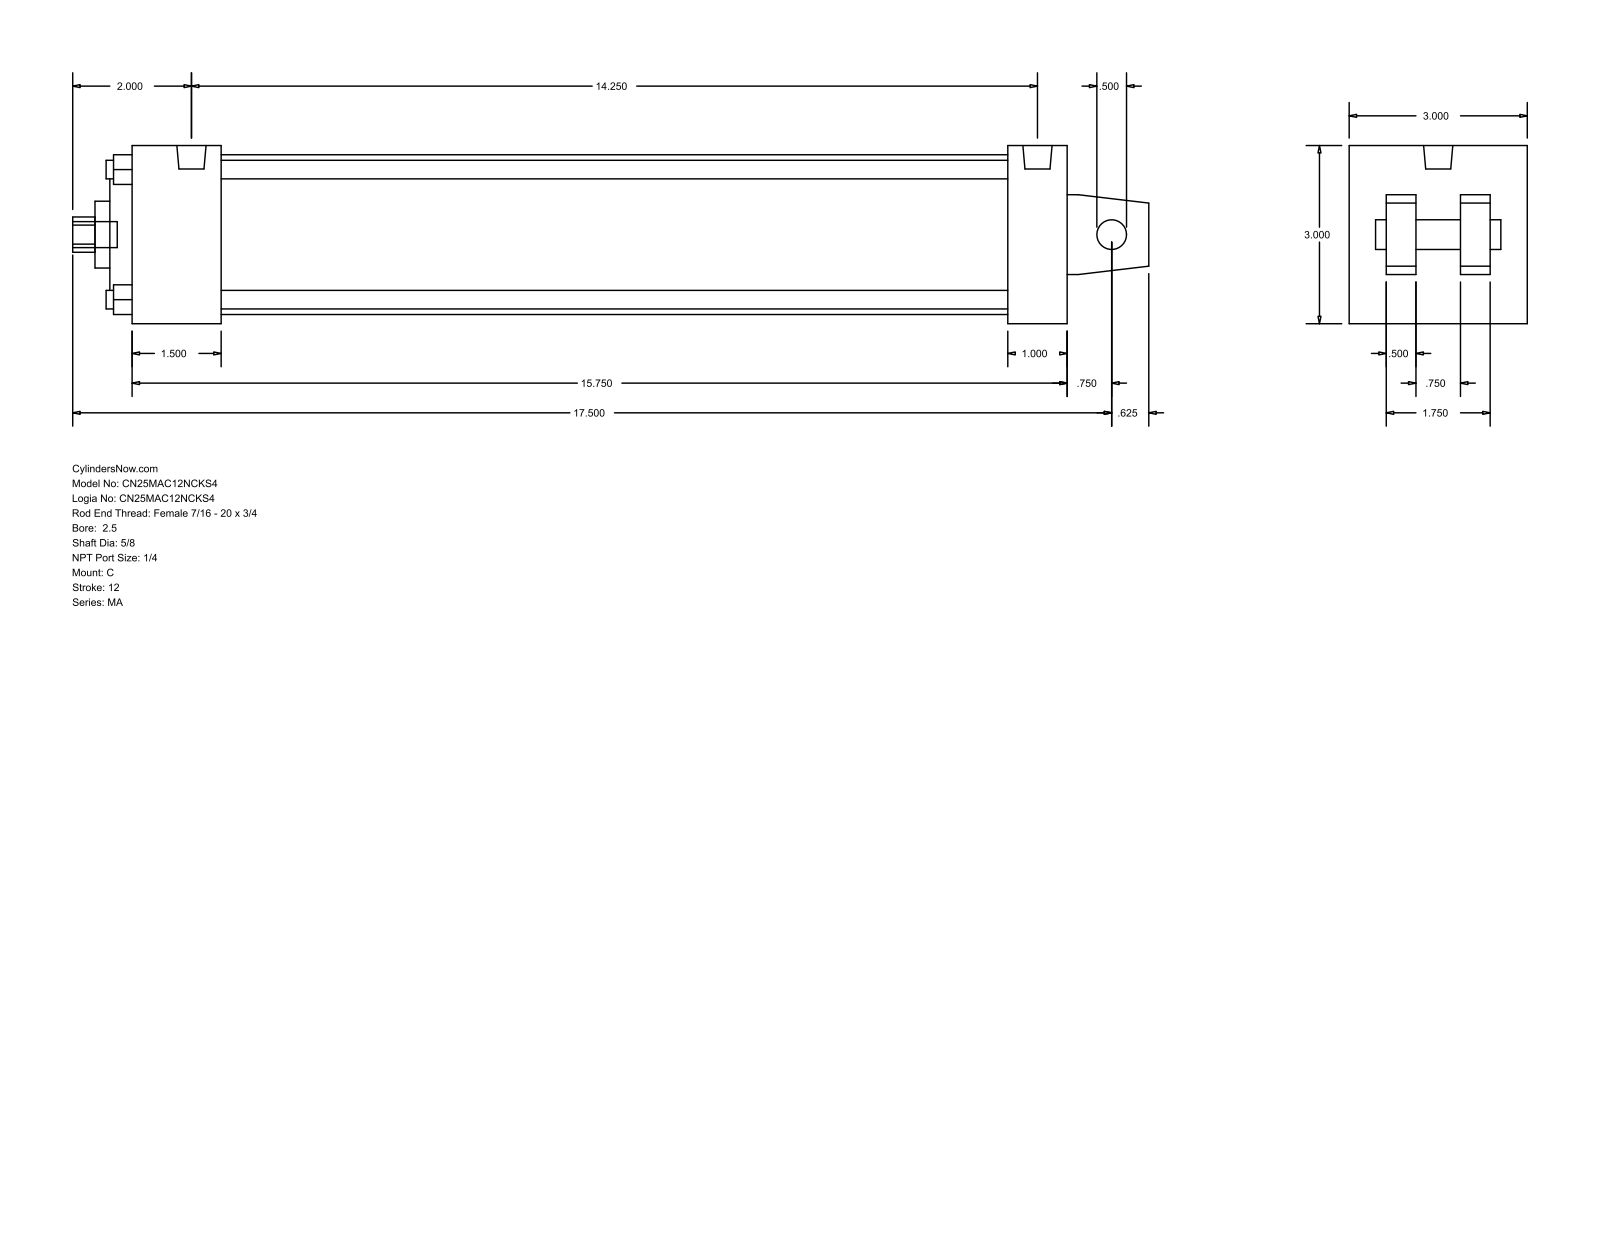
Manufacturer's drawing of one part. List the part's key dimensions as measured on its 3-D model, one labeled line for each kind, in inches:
Part name (STEP PRODUCT): MA_C__0250_0.625
STEP written by: GSSL Pune (CONFIG_CONTROL_DESIGN)
Units: inches
Bodies: 0 solids, 105 faces (77 planar, 28 cylindrical, 0 other)
Overall size (bounding box): 18.125 × 3 × 3
Round holes (diameter × count): ⌀0.313 ×4, ⌀0.5 ×1, ⌀0.625 ×1, ⌀1.125 ×1, ⌀2 ×1, ⌀2.69 ×1
Round bosses / shafts (diameter × count): ⌀0.313 ×4, ⌀0.492 ×2, ⌀0.437 ×1
Partial cylindrical surfaces — rounded edges, fillets, slot ends (radius × count): R0.297 ×1
Main face-to-face distances: 3, 15.75, 0.5, 0.625, 2.375, 1.875, 1, 1.5, 14.75, 13.25
Hole centre spacings: 1.548, 2.19, 3.097
